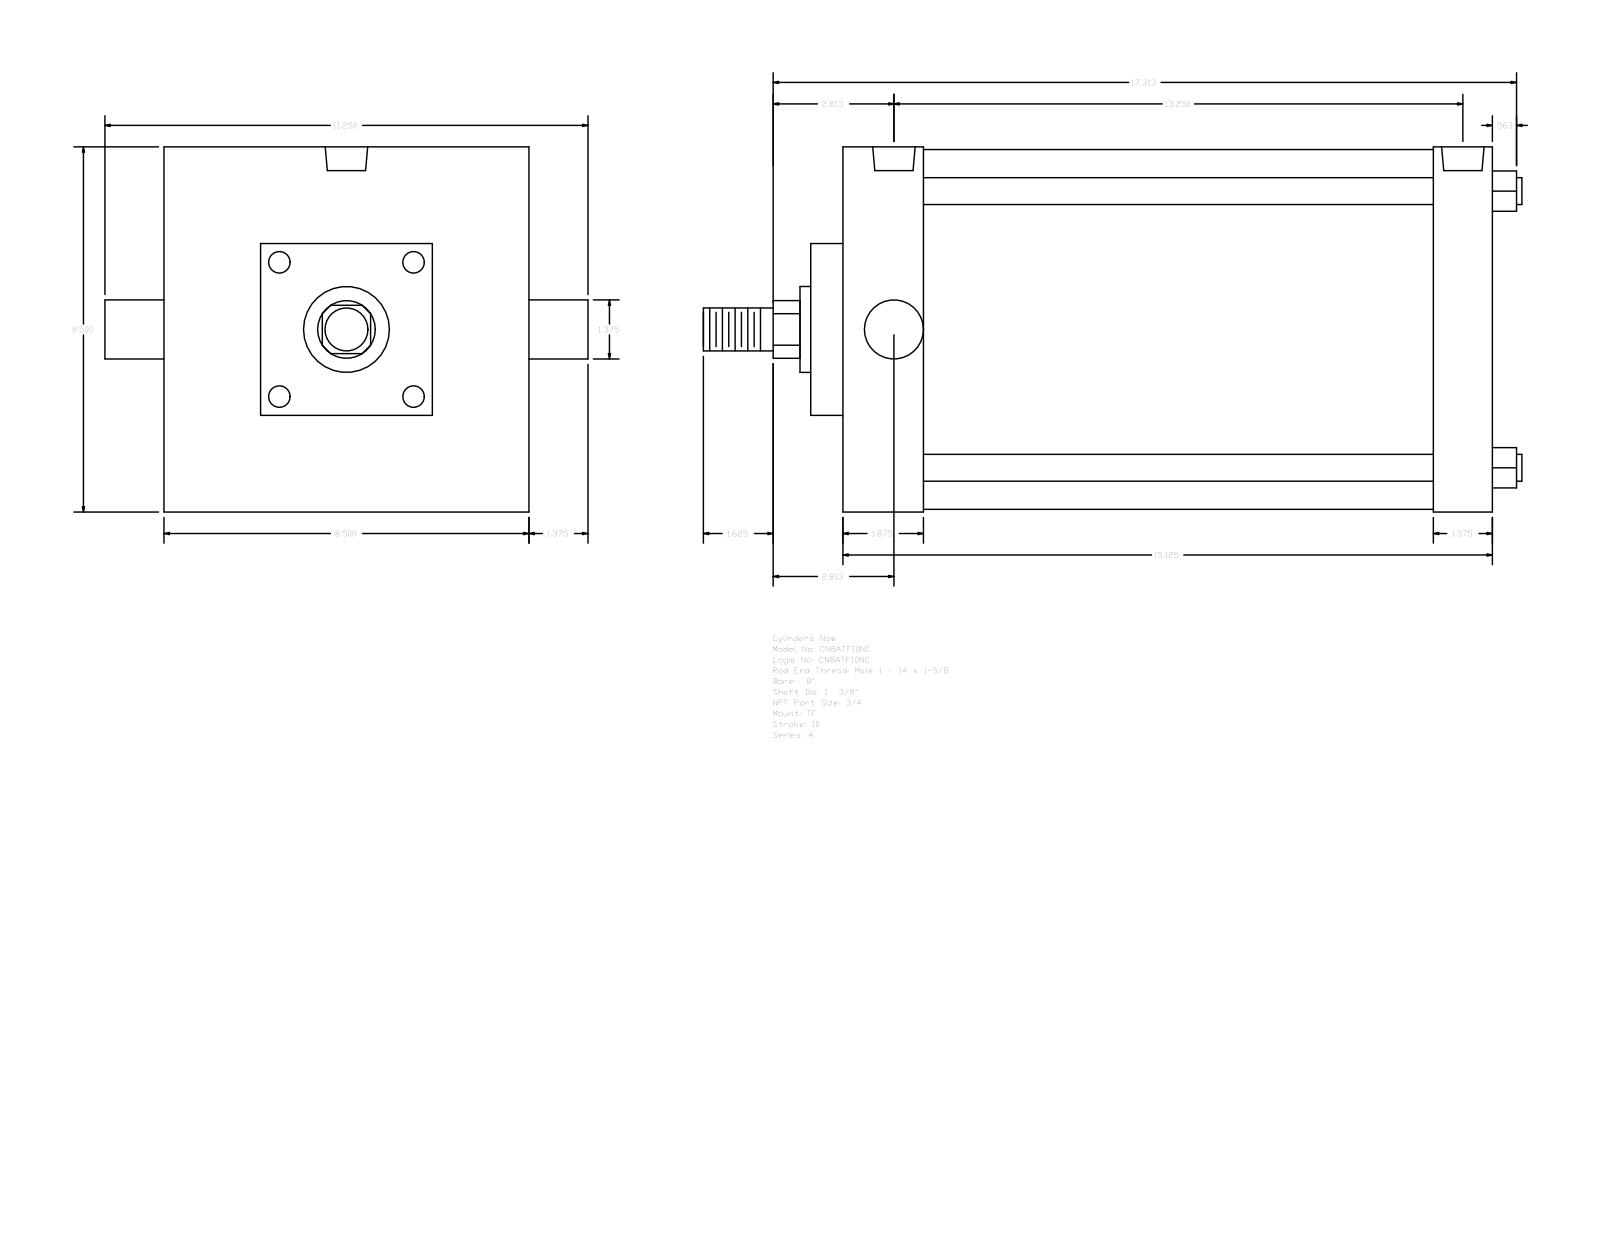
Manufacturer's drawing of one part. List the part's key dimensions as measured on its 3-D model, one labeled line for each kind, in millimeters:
Part name (STEP PRODUCT): A_TF__0800_1.375
STEP written by: GSSL Pune (CONFIG_CONTROL_DESIGN)
Units: millimetres
Bodies: 0 solids, 89 faces (65 planar, 24 cylindrical, 0 other)
Overall size (bounding box): 484.19 × 285.75 × 215.9
Round holes (diameter × count): ⌀15.08 ×3, ⌀25.12 ×2
Round bosses / shafts (diameter × count): ⌀15.88 ×4, ⌀34.92 ×2, ⌀212.72 ×1, ⌀50.8 ×1, ⌀25.4 ×1
Partial cylindrical surfaces — rounded edges, fillets, slot ends (radius × count): R17.06 ×1
Main face-to-face distances: 384.18, 215.9, 34.93, 47.63, 336.55, 349.25, 301.62, 19.04, 66.67, 368.29
Hole centre spacings: 6.35, 330.2, 323.85, 336.55
